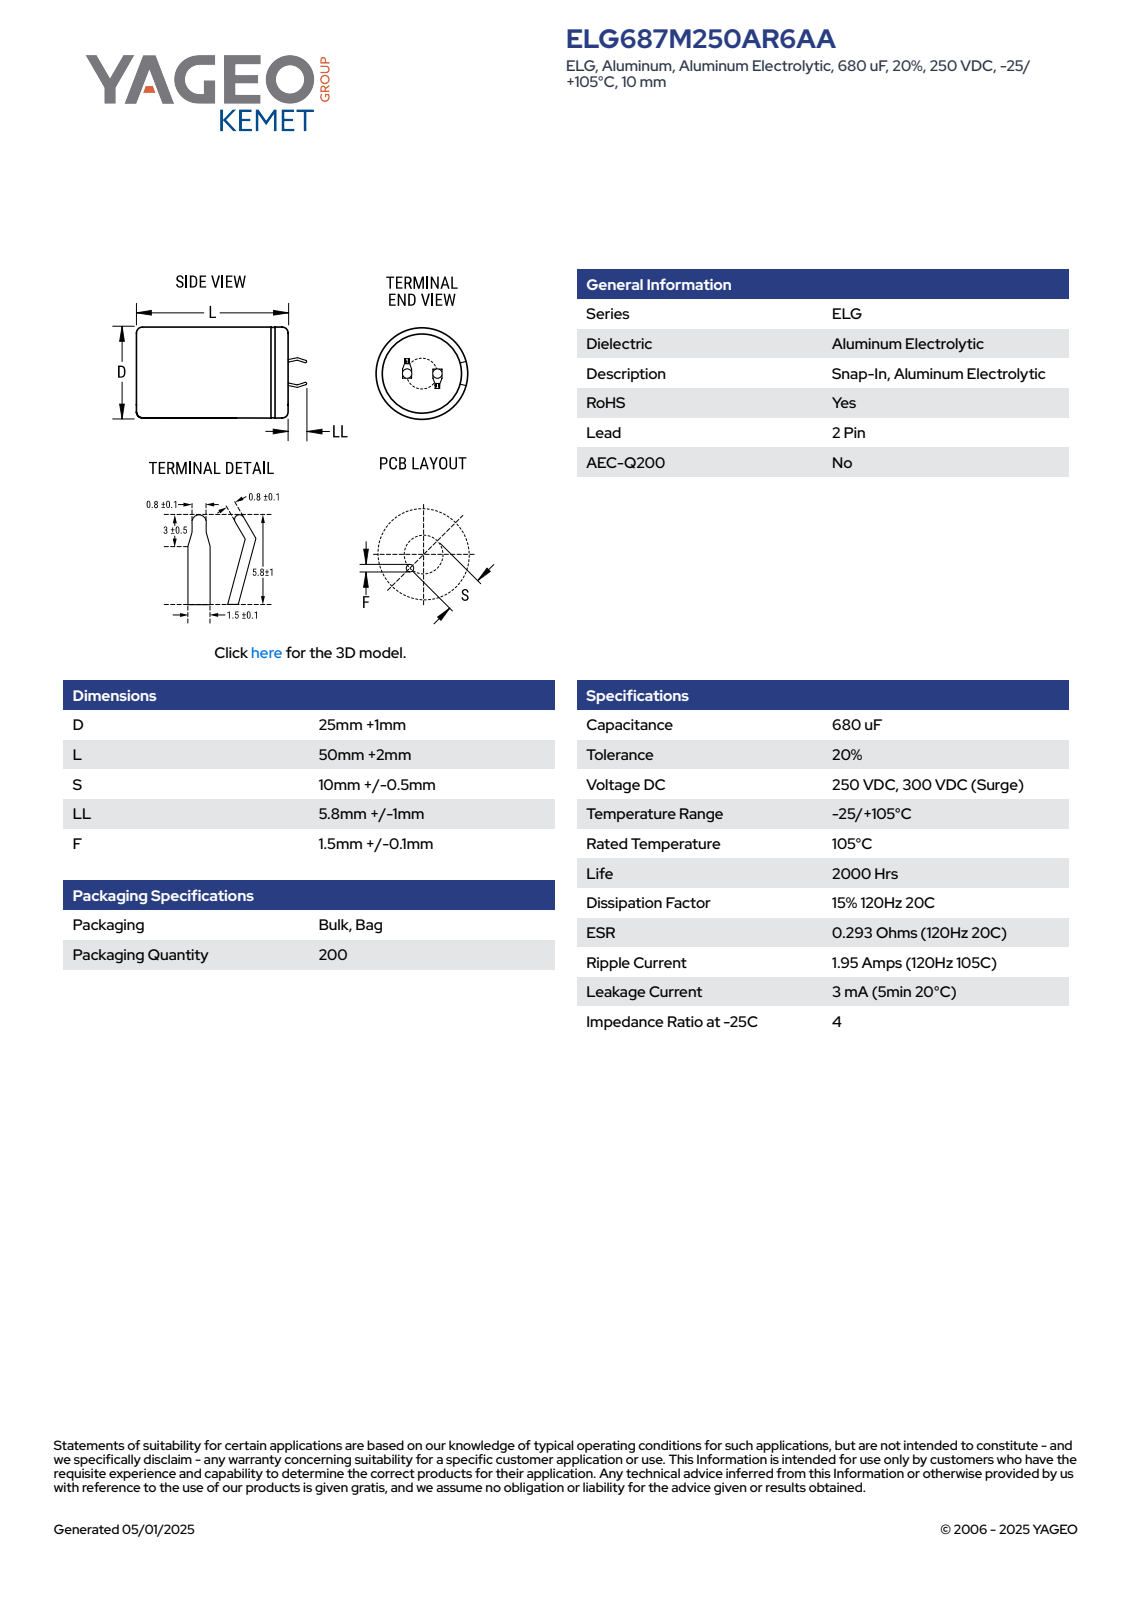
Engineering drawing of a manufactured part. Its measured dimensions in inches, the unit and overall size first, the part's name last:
Units: inches
Overall size (bounding box): 2.315 × 1.024 × 1.024
Round holes (diameter × count): ⌀0.906 ×1
Round bosses / shafts (diameter × count): ⌀1.024 ×1
Partial cylindrical surfaces — rounded edges, fillets, slot ends (radius × count): R0.511 ×1
Main face-to-face distances: 2.047, 0.024, 2.067, 0.02, 0.279, 0.3, 0.03, 0.053, 0.302, 0.255
Volume: 1.673 in³ · Surface area: 8.258 in²
Bodies: 1 solid, 100 faces (52 planar, 9 cylindrical, 39 other)
Part name (STEP PRODUCT): CARS_K2P_25X50_D26L52S10LL6.8F1.6
STEP written by: SolidWorks 2014 (AUTOMOTIVE_DESIGN)
